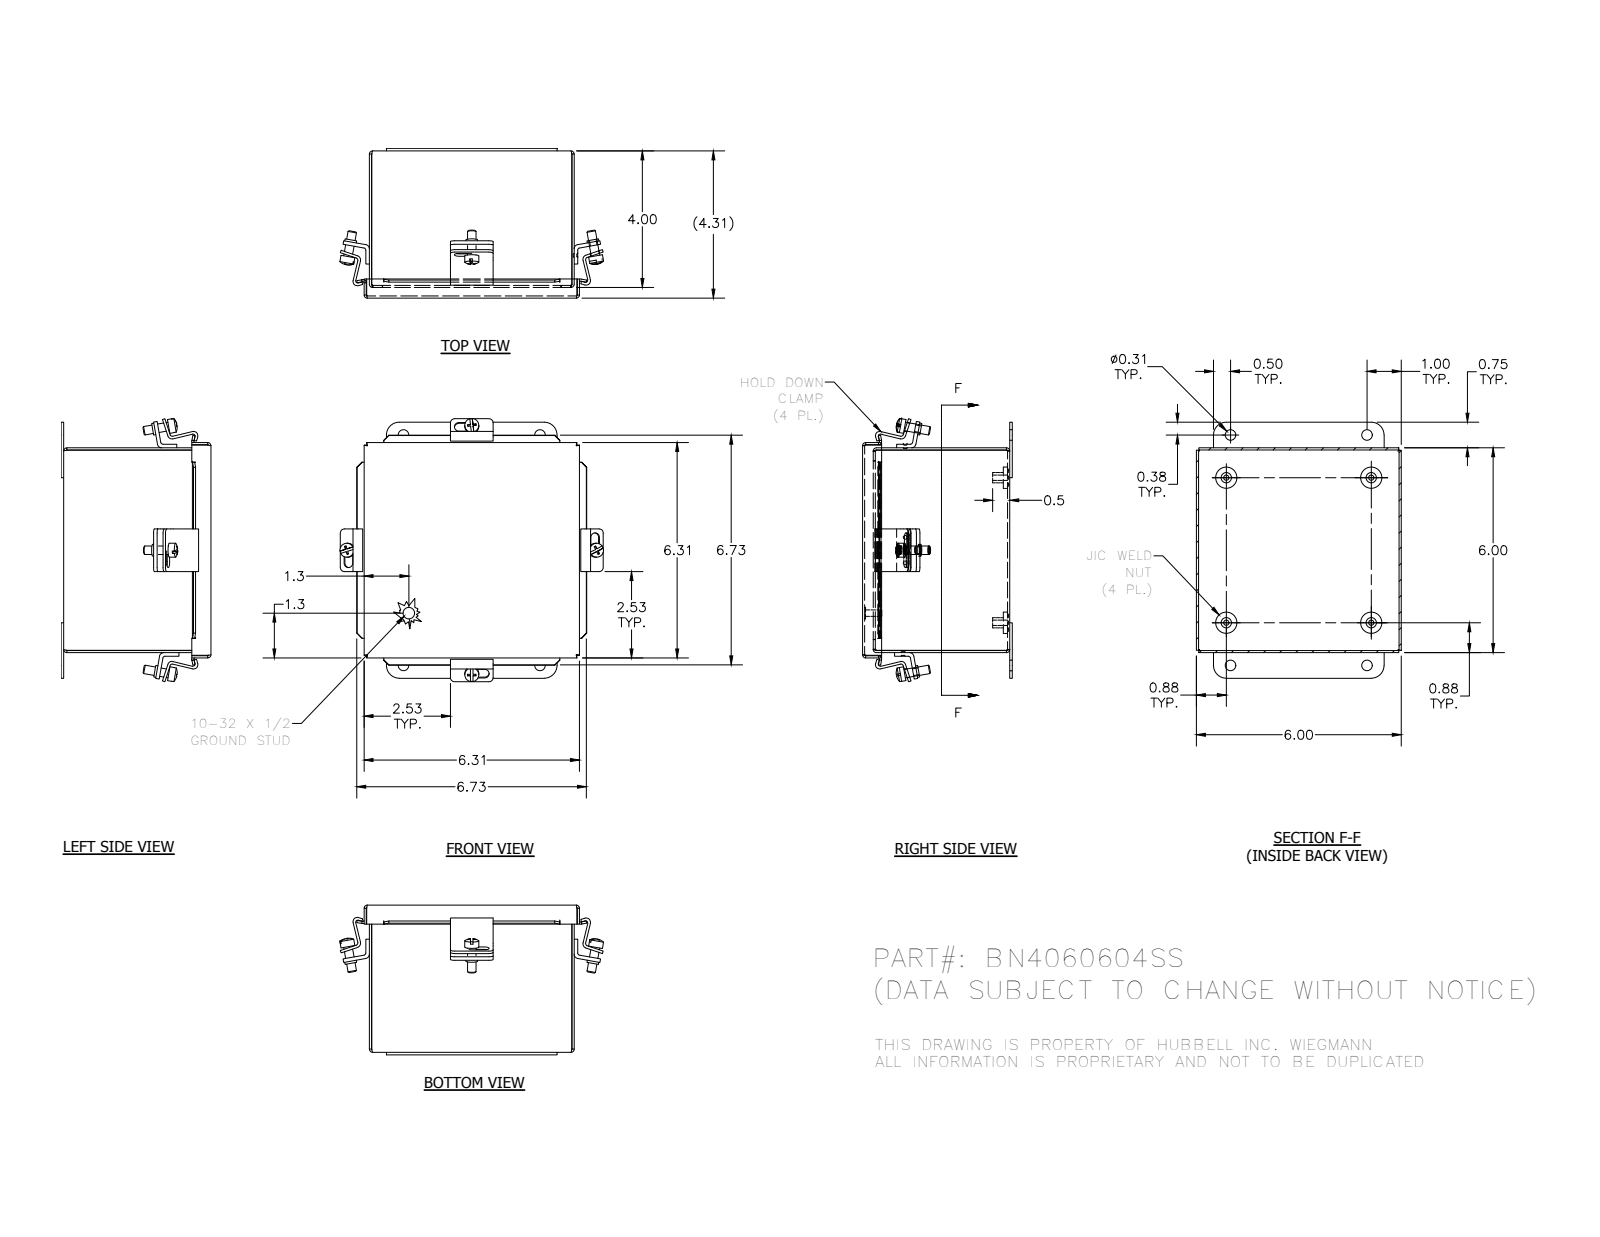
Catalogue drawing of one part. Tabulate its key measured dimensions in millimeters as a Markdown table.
| quantity | value |
| --- | --- |
| part name | C2001_1; 372135_1; C2002_1; 34973_1 (+5 more) |
| STEP written by | SolidWorks 2014 (AUTOMOTIVE_DESIGN) |
| units | millimeters |
| bodies | 21 solids, 589 faces (287 planar, 200 cylindrical, 102 other) |
| overall size | 196.2 × 195.9 × 111.5 |
| volume | 240 200 mm³ |
| surface area | 296 100 mm² |
| round holes (diameter × count) | 2.8 × 6, 4 × 4, 5 × 4, 7.9 × 4 |
| round bosses / shafts (diameter × count) | 15.9 × 4, 10.4 × 4, 8.7 × 4, 7.6 × 4, 6.4 × 4, 8.6 × 1, 4.8 × 1 |
| partial cylindrical surfaces (radius × count) | 0.8 × 16, 2.4 × 16, 3.2 × 16, 1.6 × 12, 3.2 × 12, 3.4 × 8, 9.5 × 4 |
| main face-to-face distances | 1.6, 150.8, 108, 152.4, 149.2, 109.6, 106.3, 1.9, 3.9, 154.8 |
| hole center spacings | 31.9, 108, 109.5, 139.8, 19.1, 1.6, 19.1, 101.6 |
